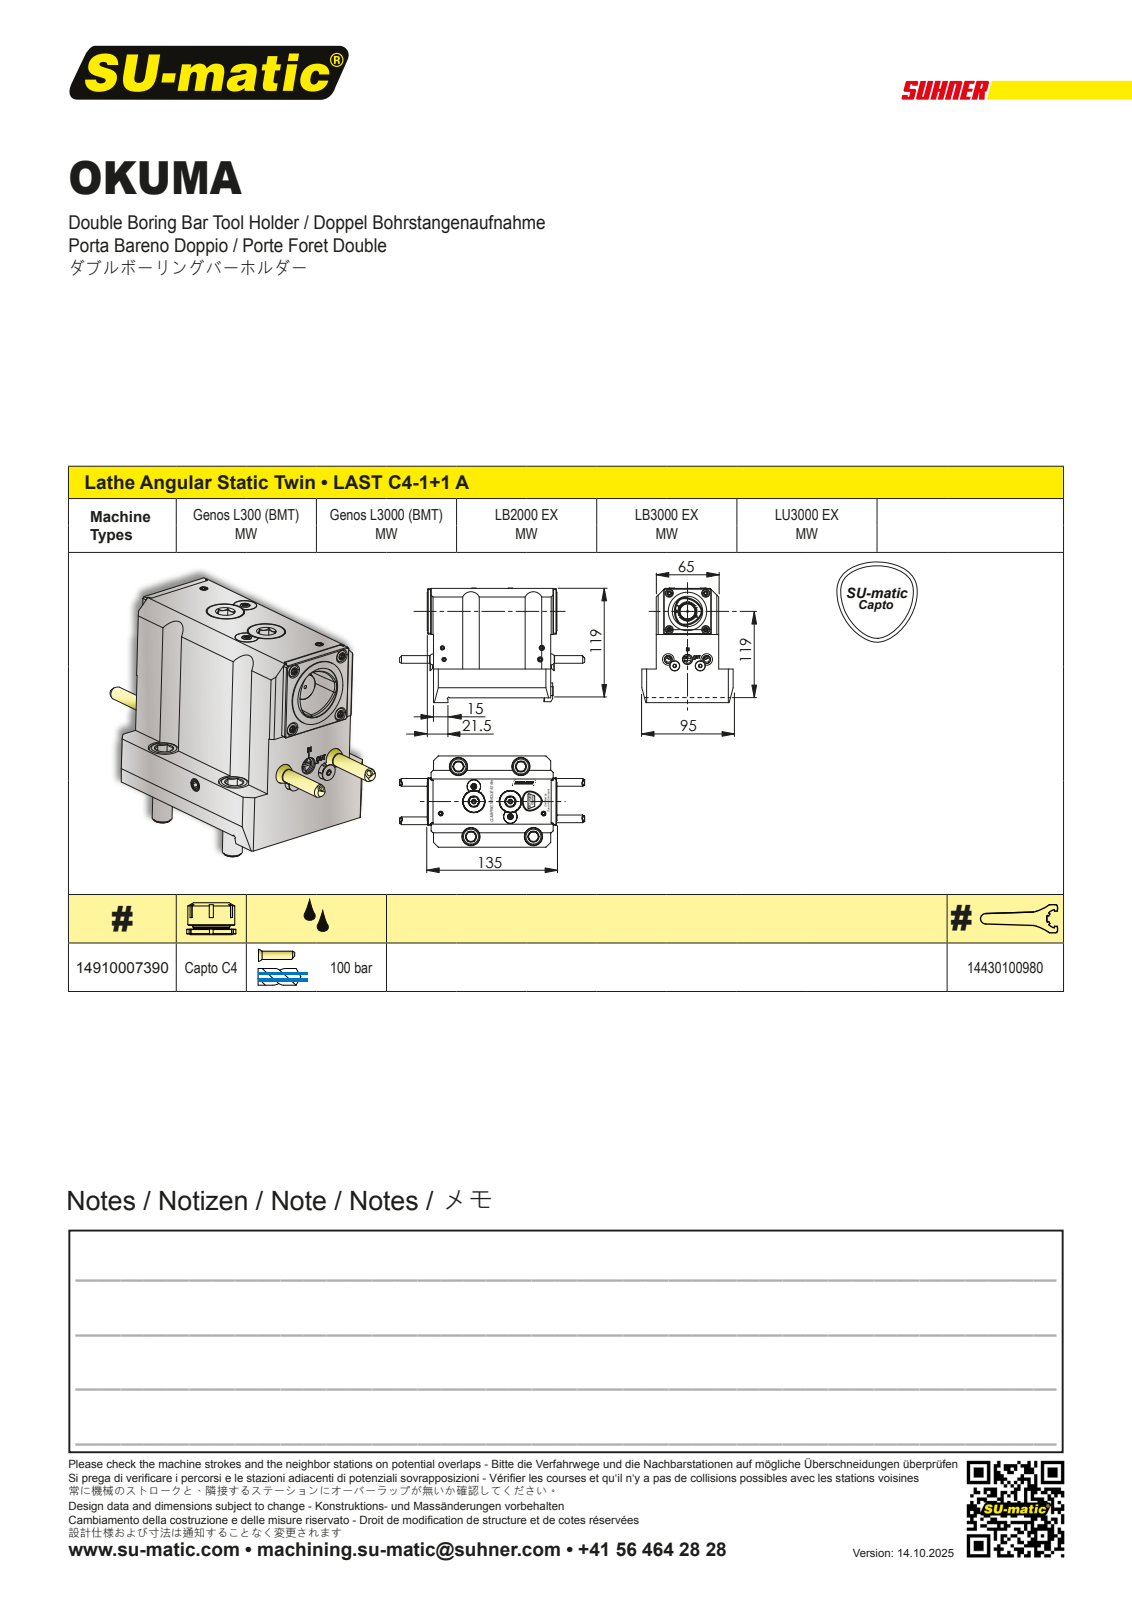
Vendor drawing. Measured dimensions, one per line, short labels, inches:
name: 14910007390dime
written by: SolidWorks 2024 (CONFIG_CONTROL_DESIGN)
unit: in
bodies: 1 solid, 101 faces (67 planar, 32 cylindrical, 2 other)
size: 5.315 × 4.685 × 3.74
volume: 60.22 in³; area: 119.3 in²
holes: 4× ⌀0.492, 4× ⌀0.748, 1× ⌀0.268, 1× ⌀0.63, 1× ⌀2.724
bosses: 1× ⌀2.402, 1× ⌀1.575
rounds: 2× R0.197, 2× R0.295
face distances: 2.559, 4.488, 0.591, 4.803, 3.15, 1.181, 3.307, 0.256, 5.059, 0.236
hole spacings: 1.764, 2.103, 2.559, 2.919, 0.696, 0.906, 1.569, 1.654
